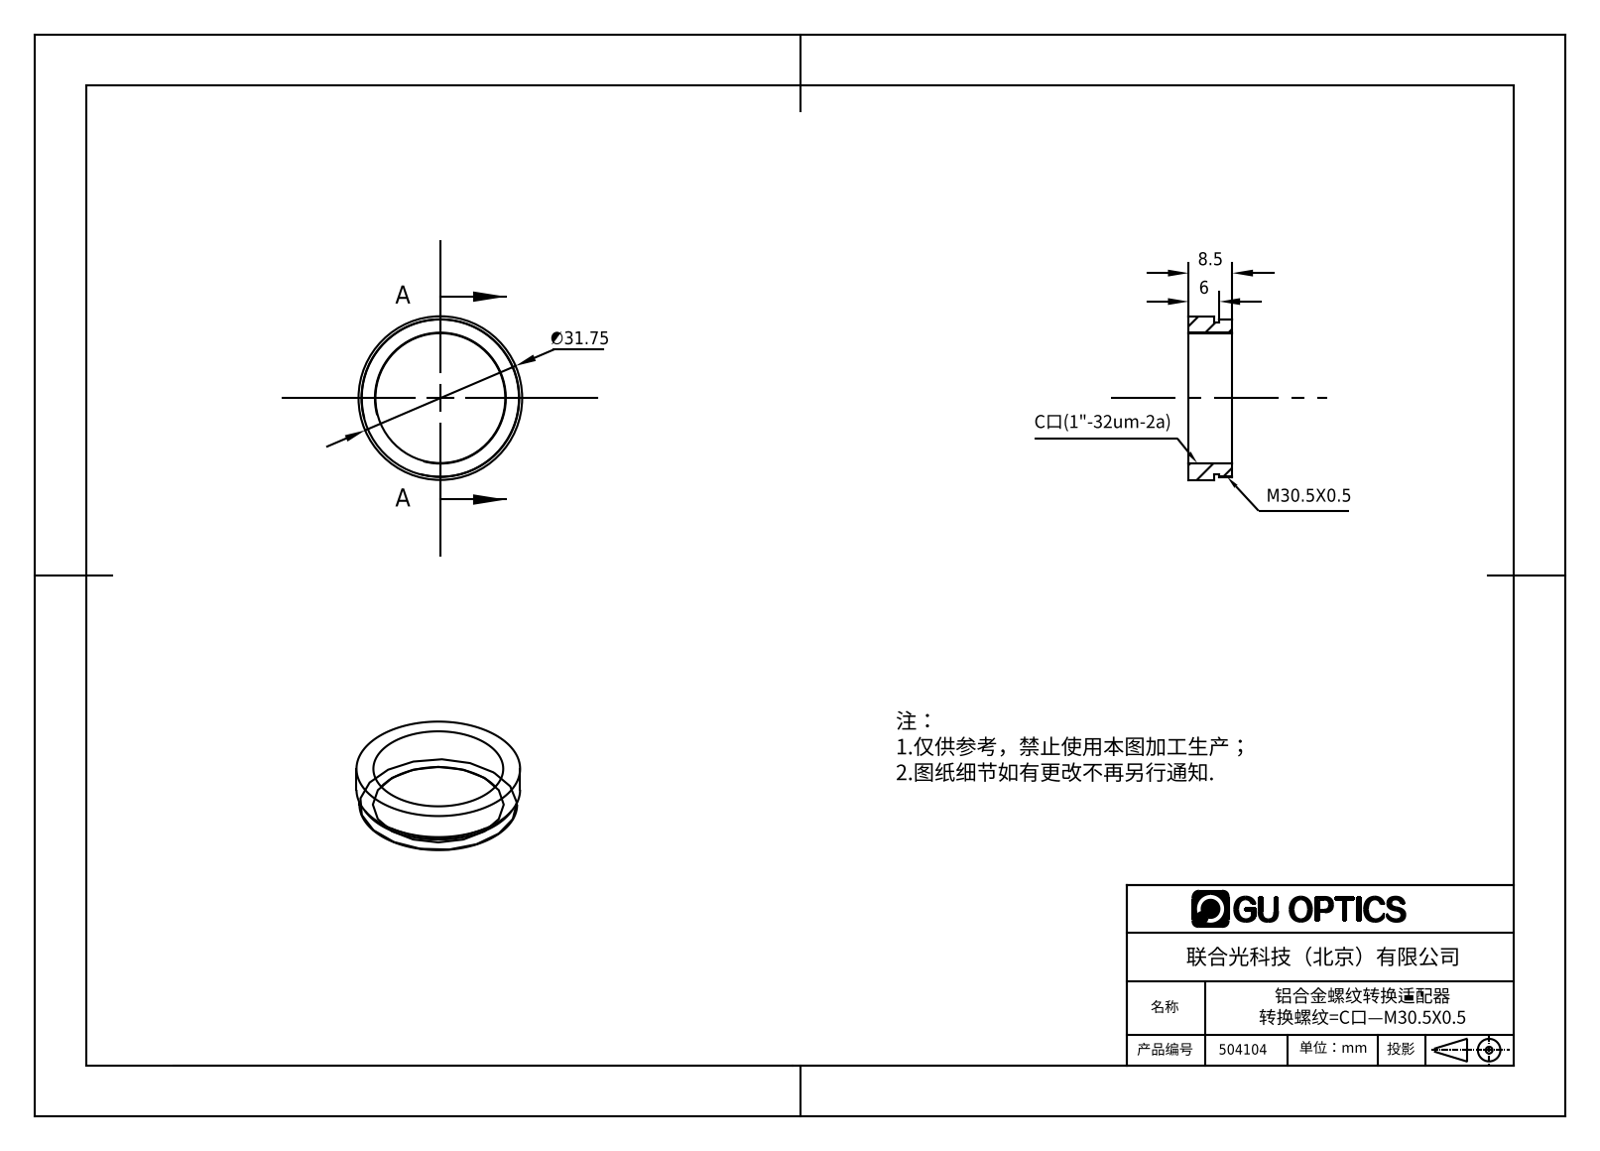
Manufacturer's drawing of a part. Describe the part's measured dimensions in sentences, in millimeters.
The part is named "504104". Its 3-D file was written by "SolidWorks 2016 (AUTOMOTIVE_DESIGN)". It is 1 solid with 12 faces: 4 planar, 8 cylindrical and 0 other. Overall it measures 31.75 by 31.75 by 8.5 millimeters. Its volume is 2 241 cubic millimeters and its surface area 2 194 square millimeters. Round holes: 1 of diameter 25.2. Round bosses or shafts: 1 of diameter 31.75, 1 of diameter 30.6, 1 of diameter 29.5. The main face-to-face distances are 8.5, 3.5, 5, 2.5, 1, 6.
